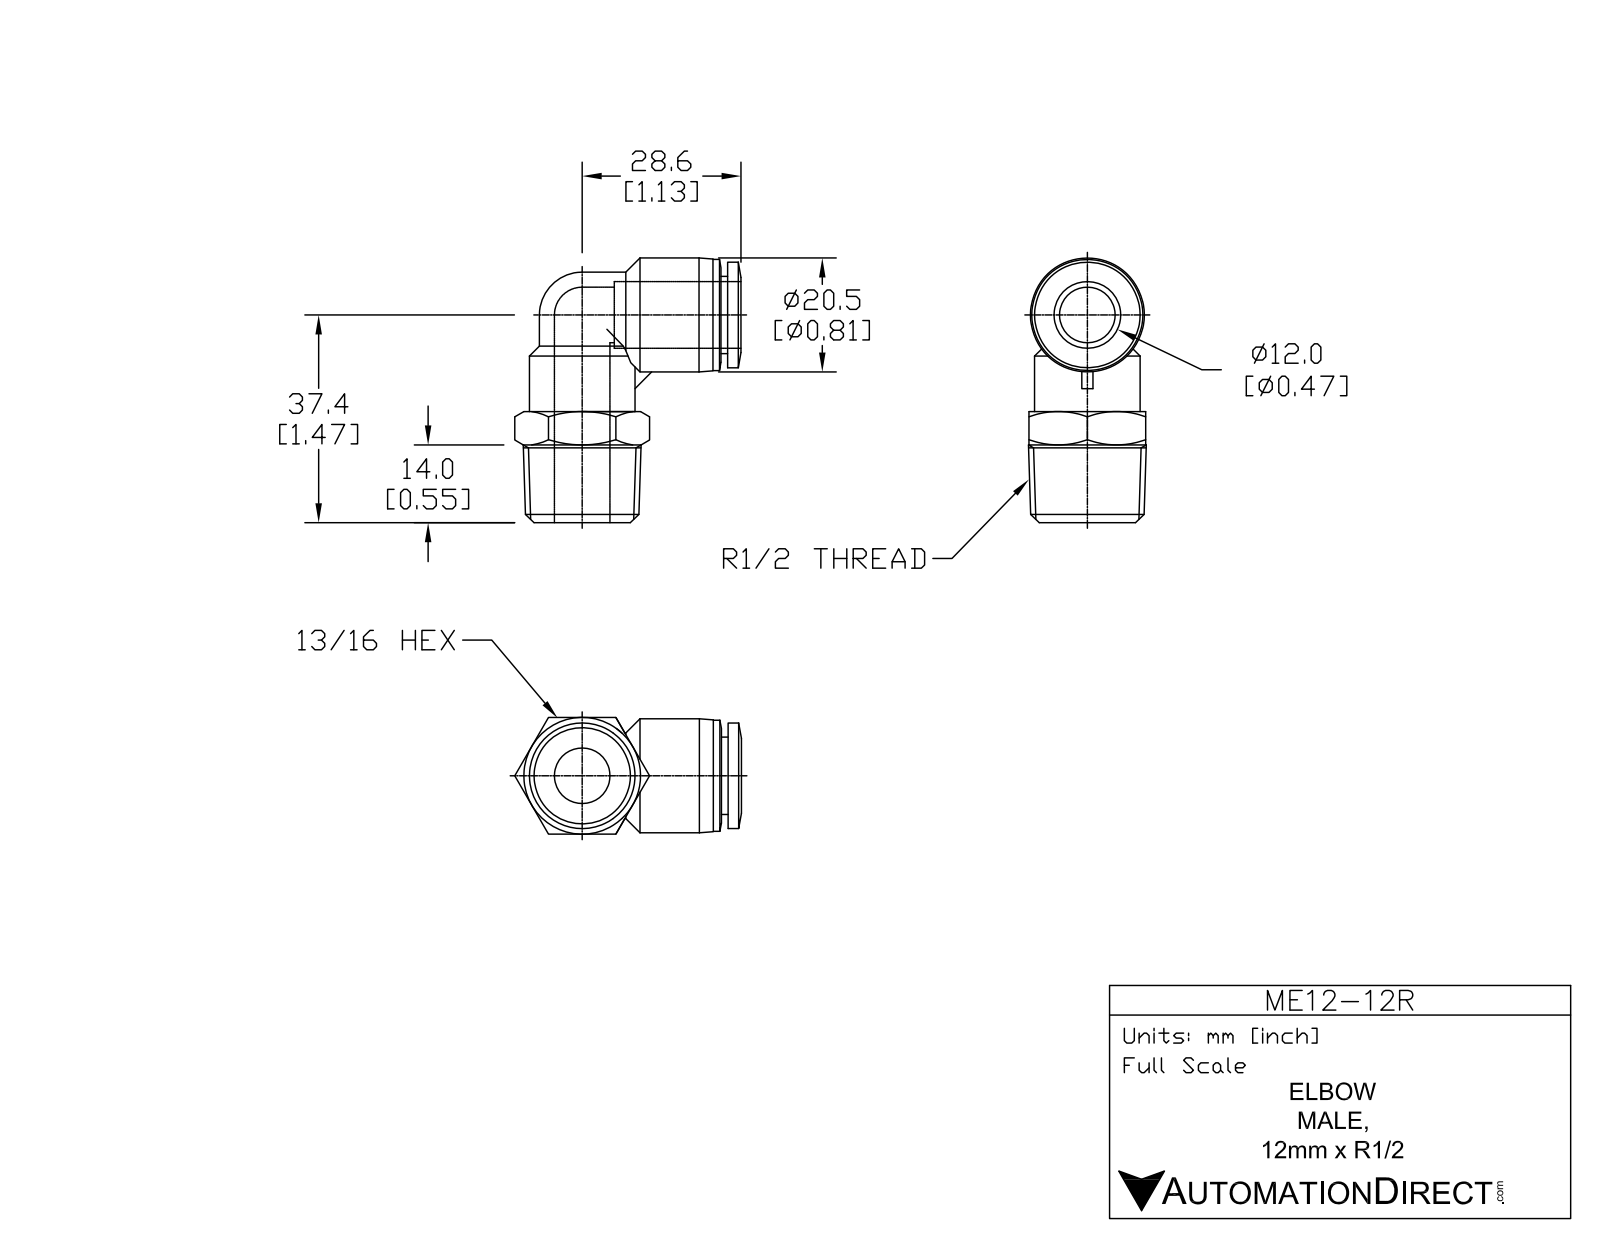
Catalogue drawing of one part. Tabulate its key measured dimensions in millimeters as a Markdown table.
| quantity | value |
| --- | --- |
| part name | ME12M-12R |
| STEP written by | SolidWorks 2015 (AUTOMOTIVE_DESIGN) |
| units | millimeters |
| bodies | 1 solid, 68 faces (16 planar, 19 cylindrical, 33 other) |
| overall size | 48.6 × 40.8 × 21 |
| volume | 12 900 mm³ |
| surface area | 7 039 mm² |
| round holes (diameter × count) | 10 × 2, 12.3 × 1 |
| round bosses / shafts (diameter × count) | 19 × 2, 20.5 × 1, 20 × 1, 15.4 × 1, 13.9 × 1 |
| partial cylindrical surfaces (radius × count) | 7.7 × 1 |
| main face-to-face distances | 21, 1.2, 20, 19.3, 20.5, 22.9, 3.6, 2.4, 9.5, 11.5 |
